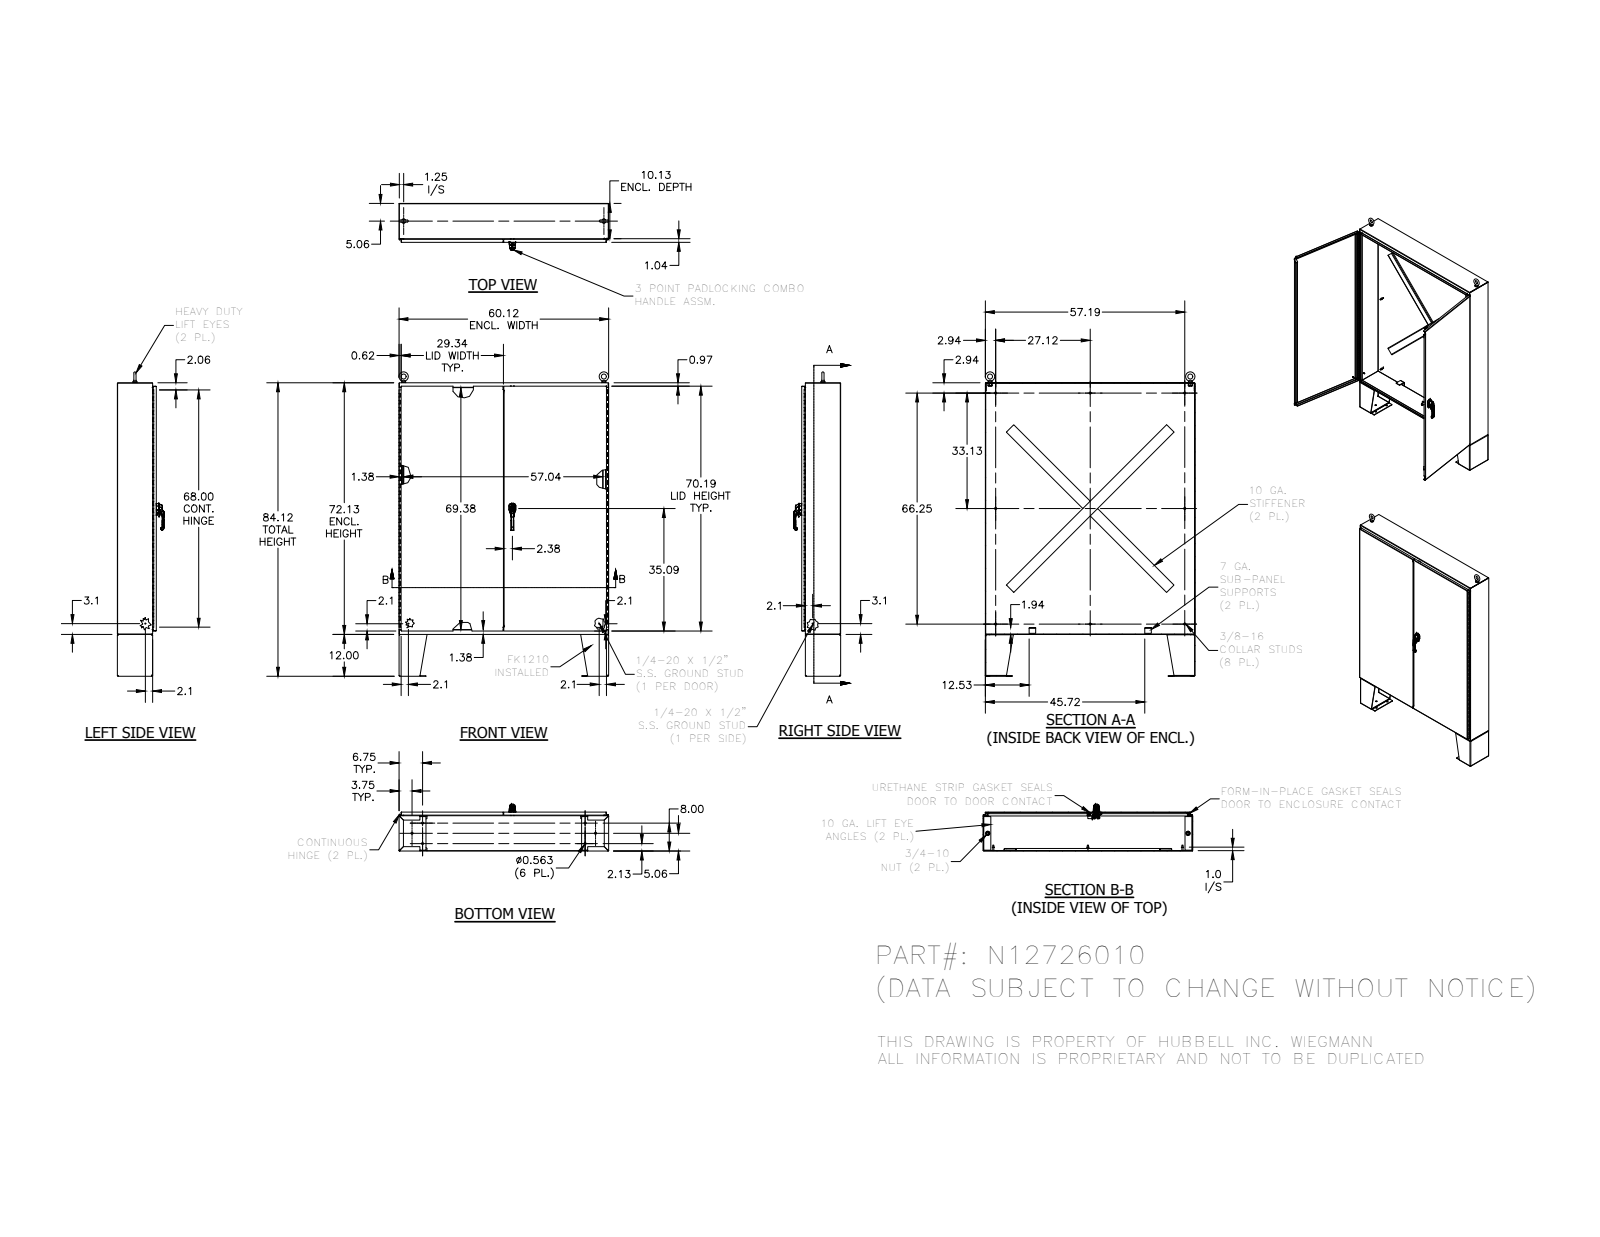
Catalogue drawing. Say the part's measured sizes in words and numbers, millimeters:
The part is named "N12726010". Its 3-D file was written by "SolidWorks 2018 (AUTOMOTIVE_DESIGN)". It is 76 solids with 2596 faces: 1528 planar, 768 cylindrical and 300 other. Overall it measures 2216.1 by 1527.2 by 338.8 millimeters. Its volume is 23 370 000 cubic millimeters and its surface area 18 570 000 square millimeters. Round holes: 18 of diameter 14.3, 8 of diameter 7, 4 of diameter 5.1, 3 of diameter 7.1, 2 of diameter 3.2, 2 of diameter 3.2, 2 of diameter 6.1, 2 of diameter 6.4, 2 of diameter 6.4, 2 of diameter 10.2, 2 of diameter 11.4, 2 of diameter 16.3. Round bosses or shafts: 8 of diameter 8.4, 6 of diameter 15.9, 5 of diameter 6.4, 3 of diameter 8.6, 2 of diameter 31.8, 2 of diameter 28.4, 2 of diameter 25.4, 2 of diameter 19.1. Partial cylindrical surfaces (rounded edges, fillets, slot ends): 24 of radius 0.8, 23 of radius 2.4, 22 of radius 5.6, 18 of radius 1.3, 16 of radius 0.6, 15 of radius 3.2, 13 of radius 0.8, 8 of radius 1.7. The main face-to-face distances are 2.4, 281.1, 278.7, 283.5, 1524.8, 1829.6, 1527.2, 1522.4, 3.2, 3.2. The hole center spacings are 51.8, 106.6, 127, 156.3, 181.6, 222.3, 256, 1178.5.
